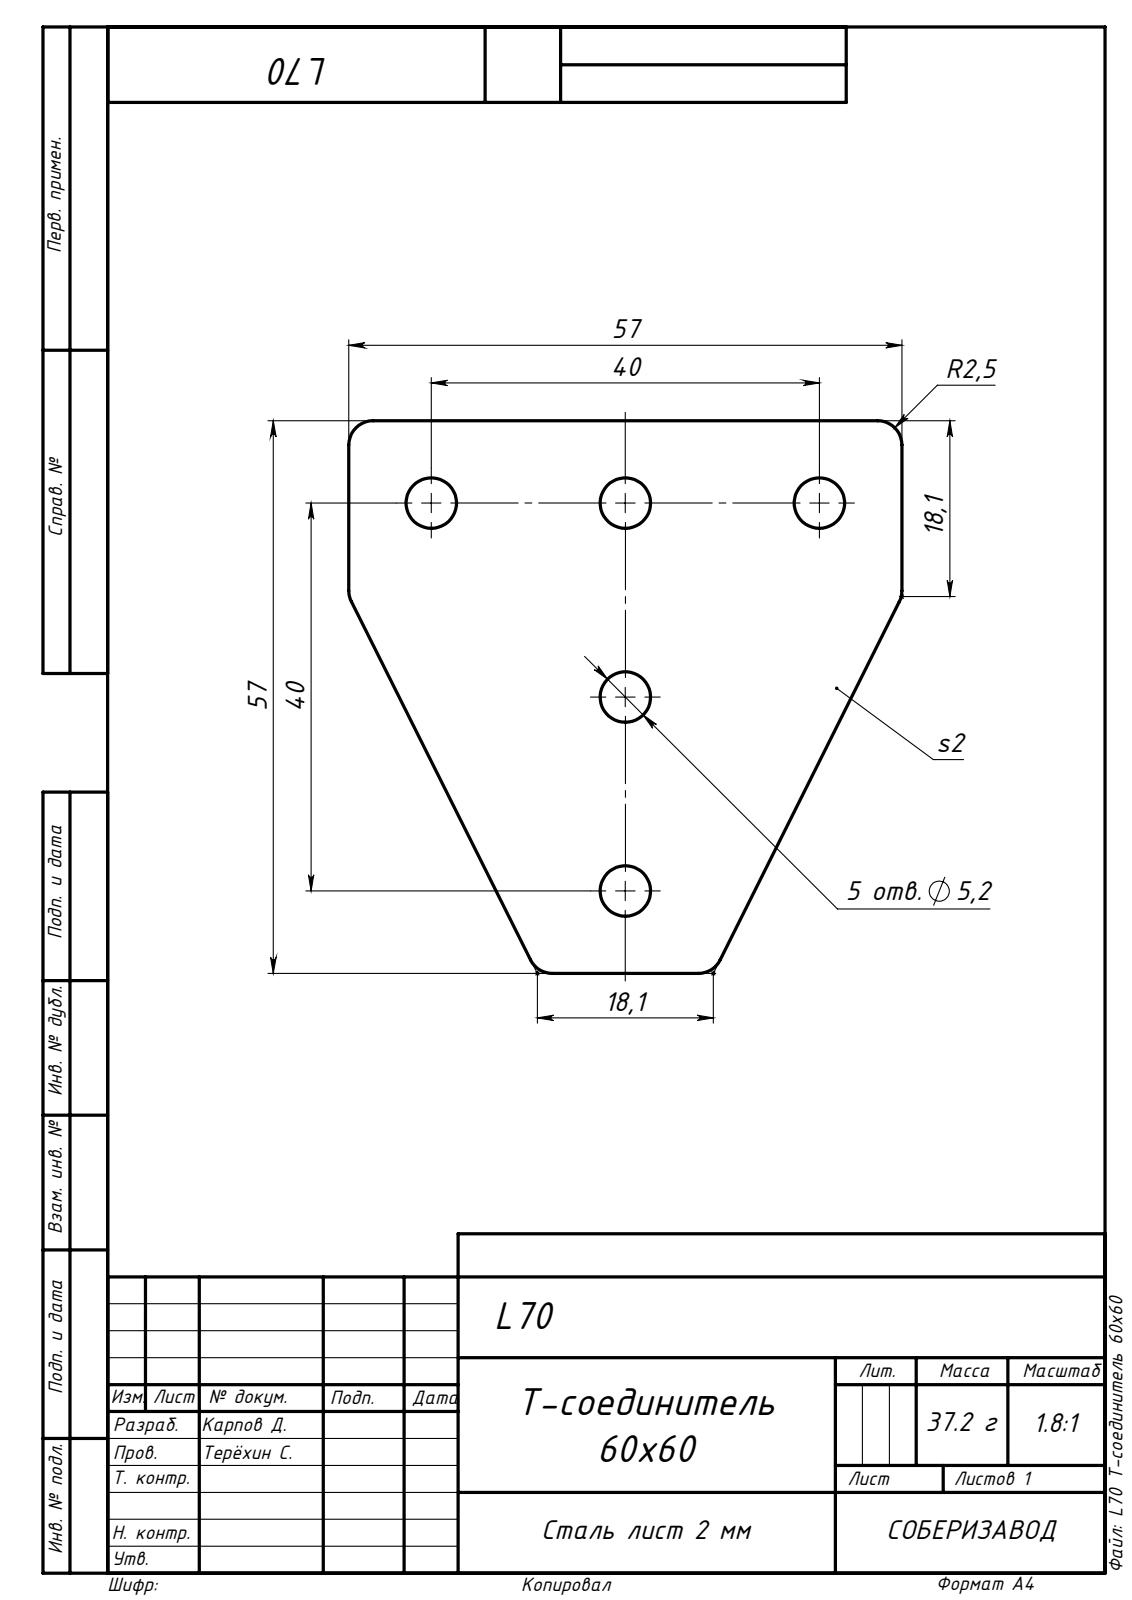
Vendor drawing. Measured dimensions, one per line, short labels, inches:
name: L70 Т-соединитель 60х60
written by: SolidWorks 2019 (AUTOMOTIVE_DESIGN)
unit: in
bodies: 1 solid, 24 faces (8 planar, 16 cylindrical, 0 other)
size: 2.244 × 2.244 × 0.079
volume: 0.291 in³; area: 8.251 in²
holes: 5× ⌀0.205
rounds: 6× R0.098
face distances: 0.079, 2.244
hole spacings: 0.787, 1.113, 1.575, 1.761
